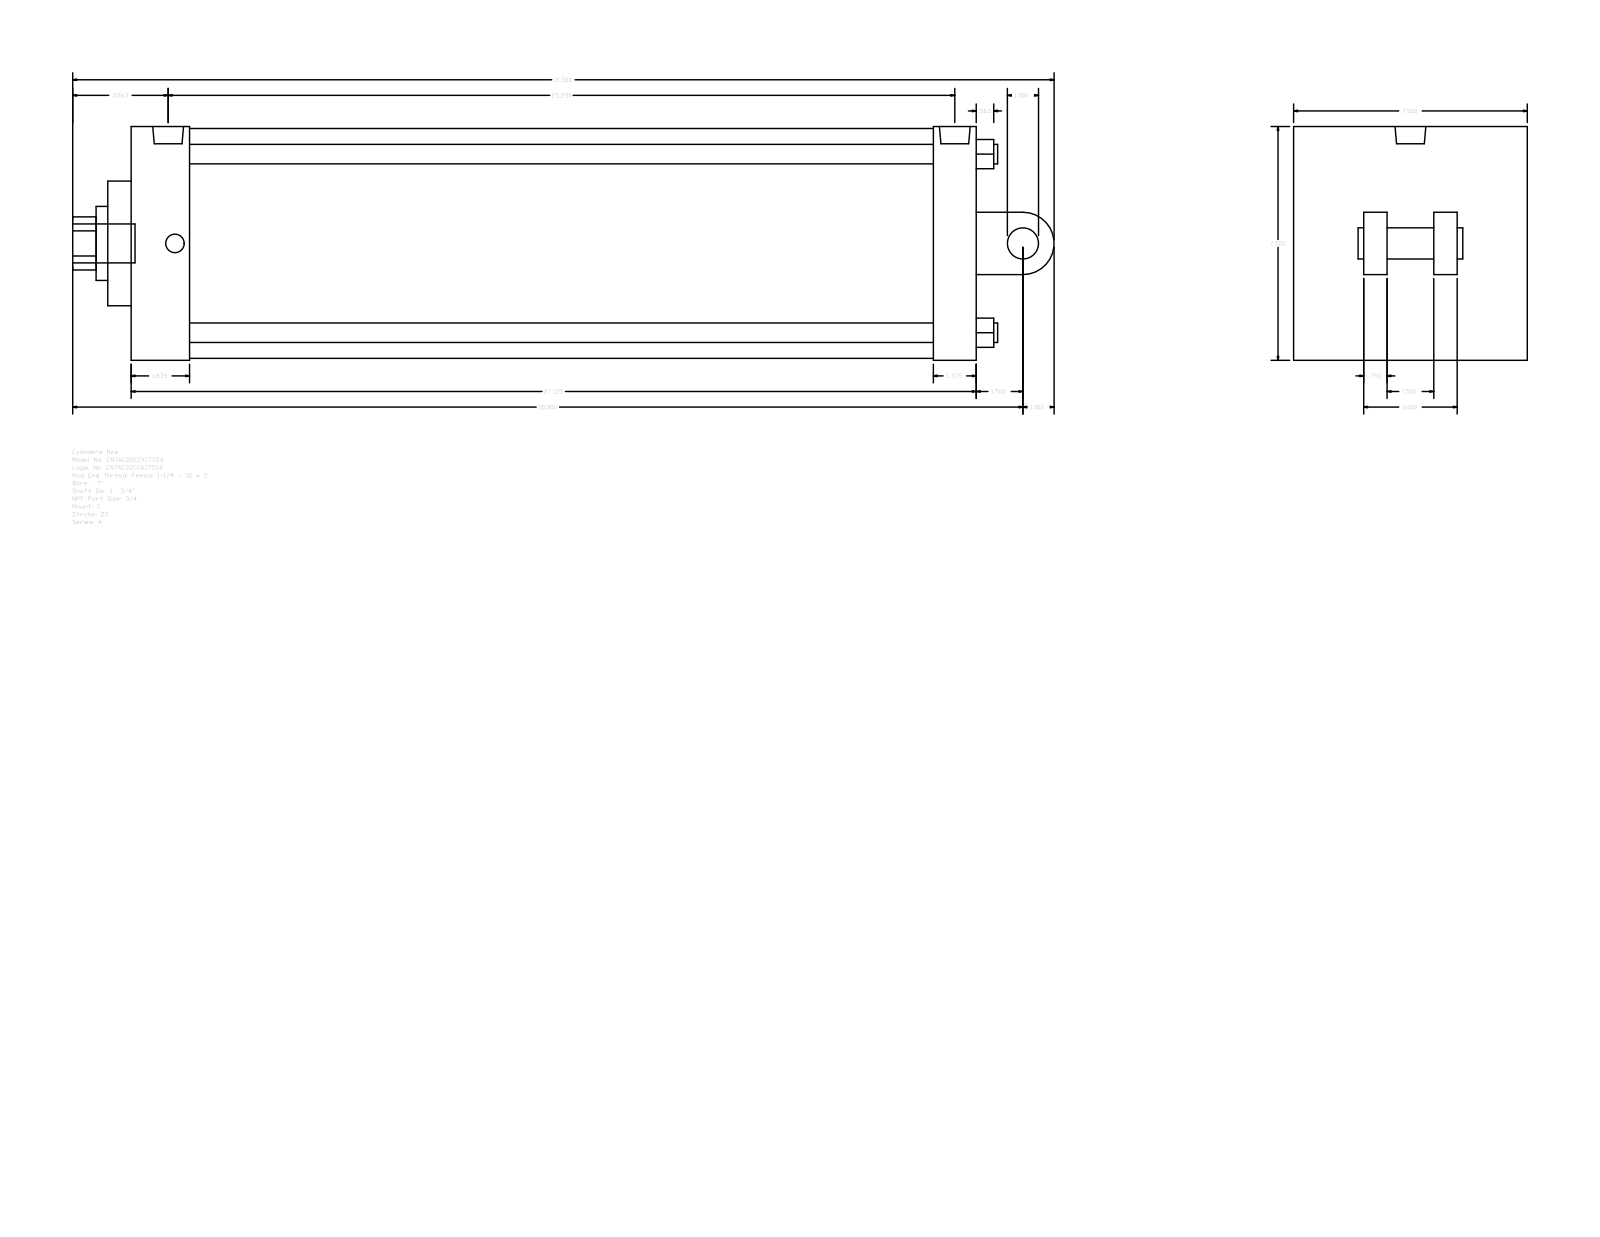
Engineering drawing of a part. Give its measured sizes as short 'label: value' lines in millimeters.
name: A_C__0700_1.75
written by: GSSL Pune (CONFIG_CONTROL_DESIGN)
unit: mm
bodies: 0 solids, 104 faces (75 planar, 29 cylindrical, 0 other)
size: 800.1 × 190.5 × 190.5
holes: 4× ⌀15.88, 2× ⌀15.08, 1× ⌀25.12, 1× ⌀44.45, 1× ⌀60.33, 1× ⌀187.32
bosses: 2× ⌀15.08, 1× ⌀31.75, 1× ⌀25.4, 1× ⌀25.12
rounds: 1× R21.63, 1× R25.4
face distances: 190.5, 688.98, 19.05, 76.2, 57.15, 44.45, 47.63, 641.35, 654.05, 606.42
hole spacings: 102.91, 145.54, 205.82, 5.56
